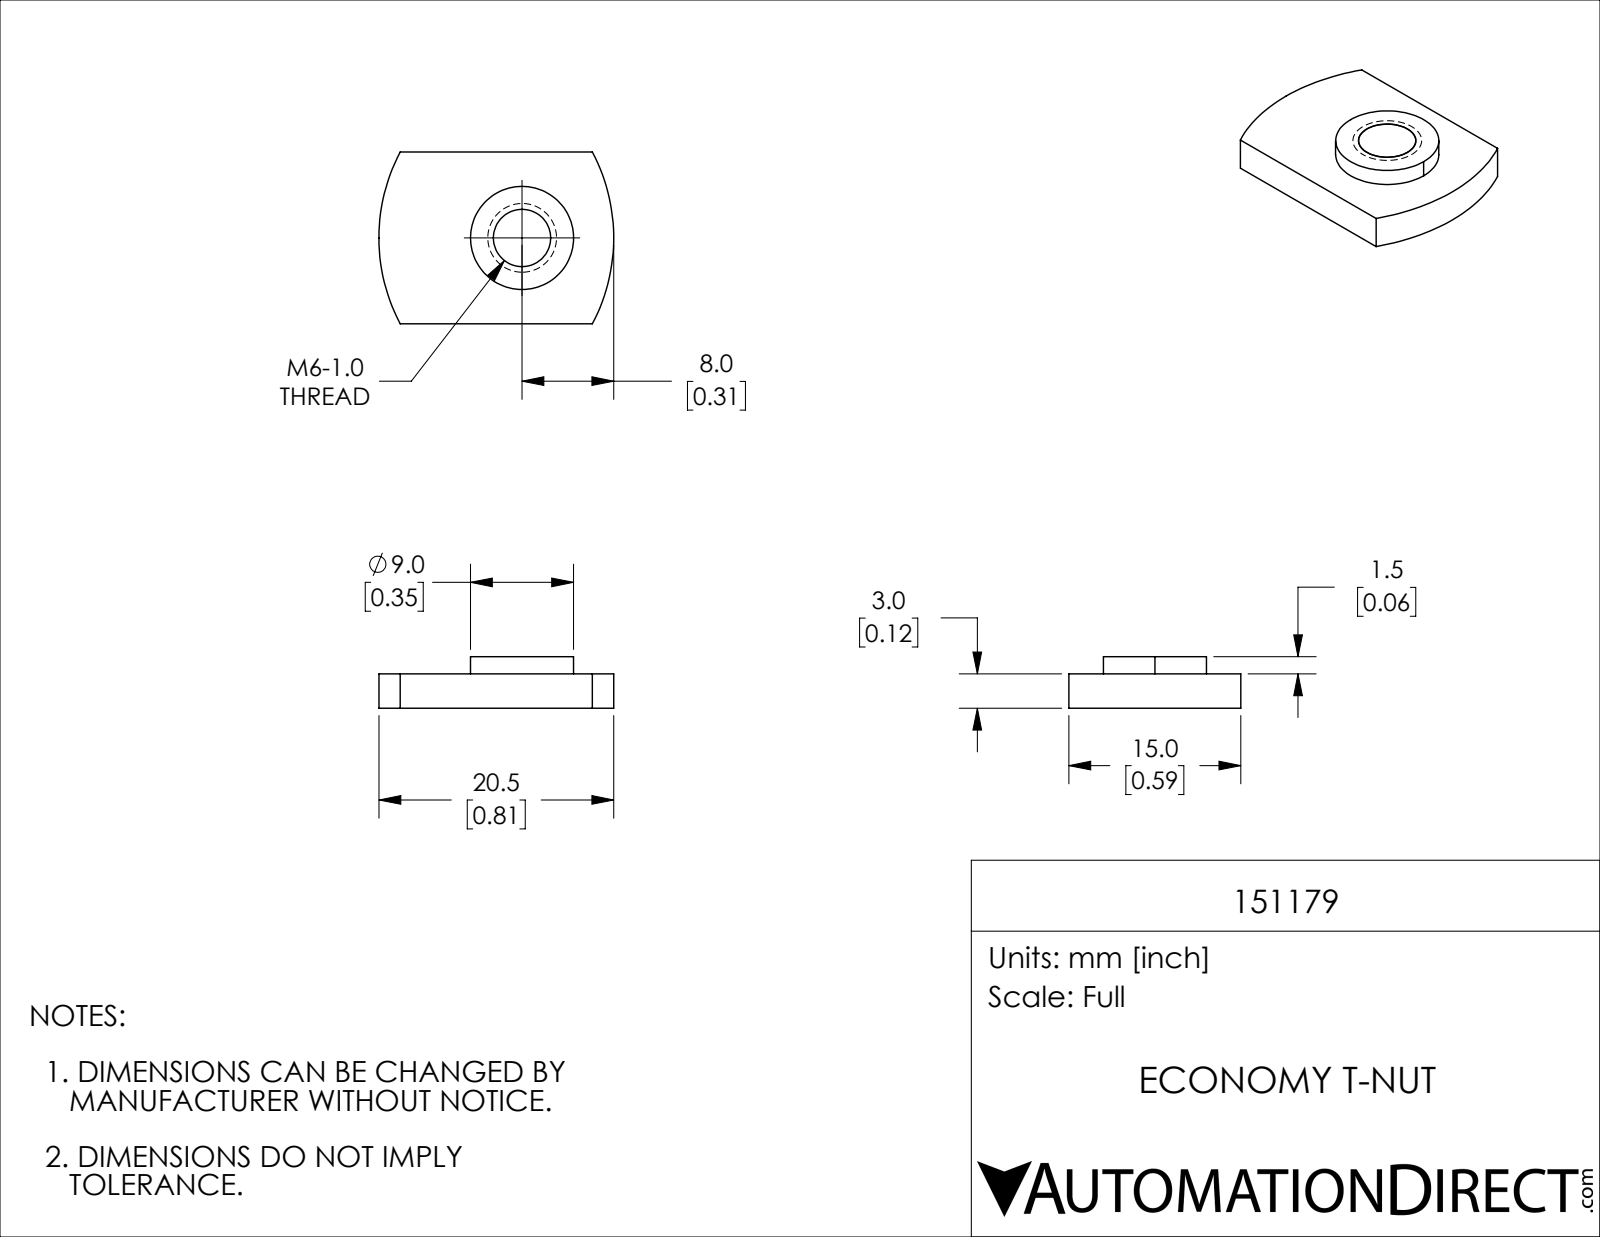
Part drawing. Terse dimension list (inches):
name: 151179
written by: SolidWorks 2021 (CONFIG_CONTROL_DESIGN)
unit: in
bodies: 1 solid, 12 faces (5 planar, 7 cylindrical, 0 other)
size: 0.807 × 0.591 × 0.177
volume: 0.053 in³; area: 1.31 in²
holes: 1× ⌀0.197
bosses: 1× ⌀0.354
rounds: 2× R0.63
face distances: 0.118, 0.591, 0.177, 0.059
